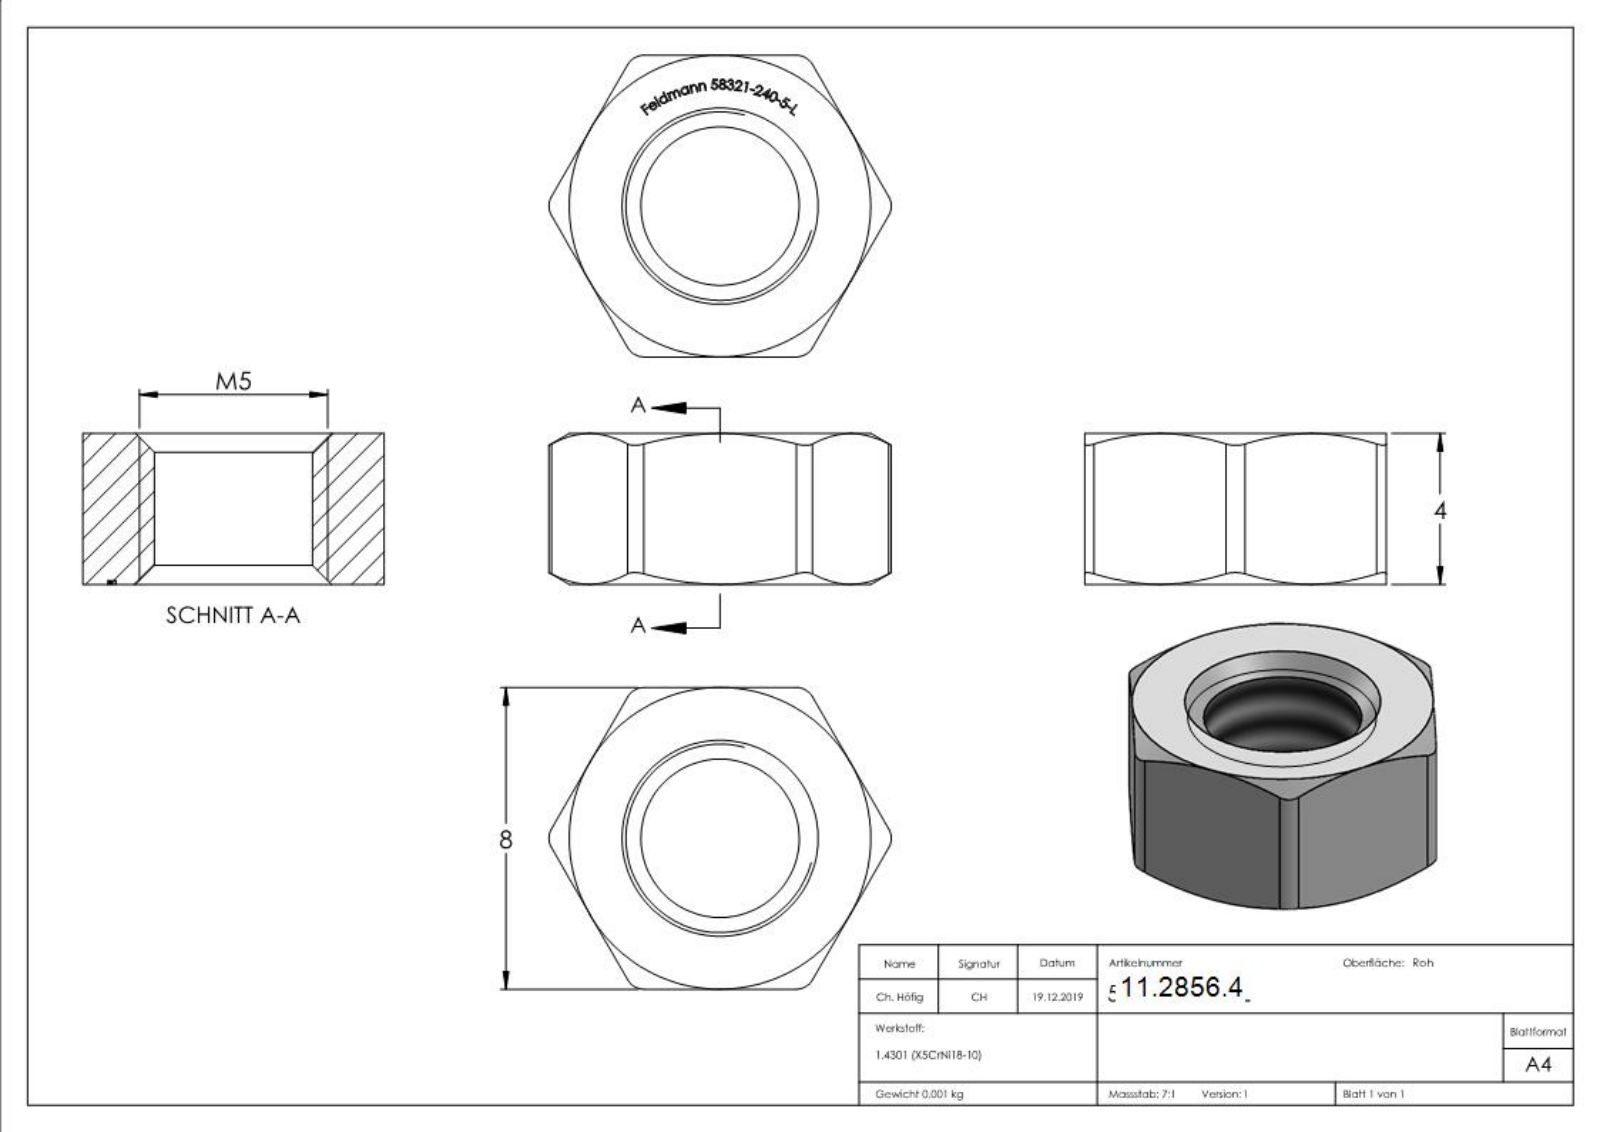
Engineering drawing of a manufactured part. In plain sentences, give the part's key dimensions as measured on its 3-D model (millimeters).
The part is named "58321-240-5-L". Its 3-D file was written by "SolidWorks 2015 (CONFIG_CONTROL_DESIGN)". It is 1 solid with 29 faces: 8 planar, 7 cylindrical and 14 other. Overall it measures 22 by 9.08 by 8 millimeters. Its volume is 161 cubic millimeters and its surface area 233 square millimeters. Round holes: 1 of diameter 4.2. Partial cylindrical surfaces (rounded edges, fillets, slot ends): 6 of radius 0.5. The main face-to-face distances are 8, 4.
